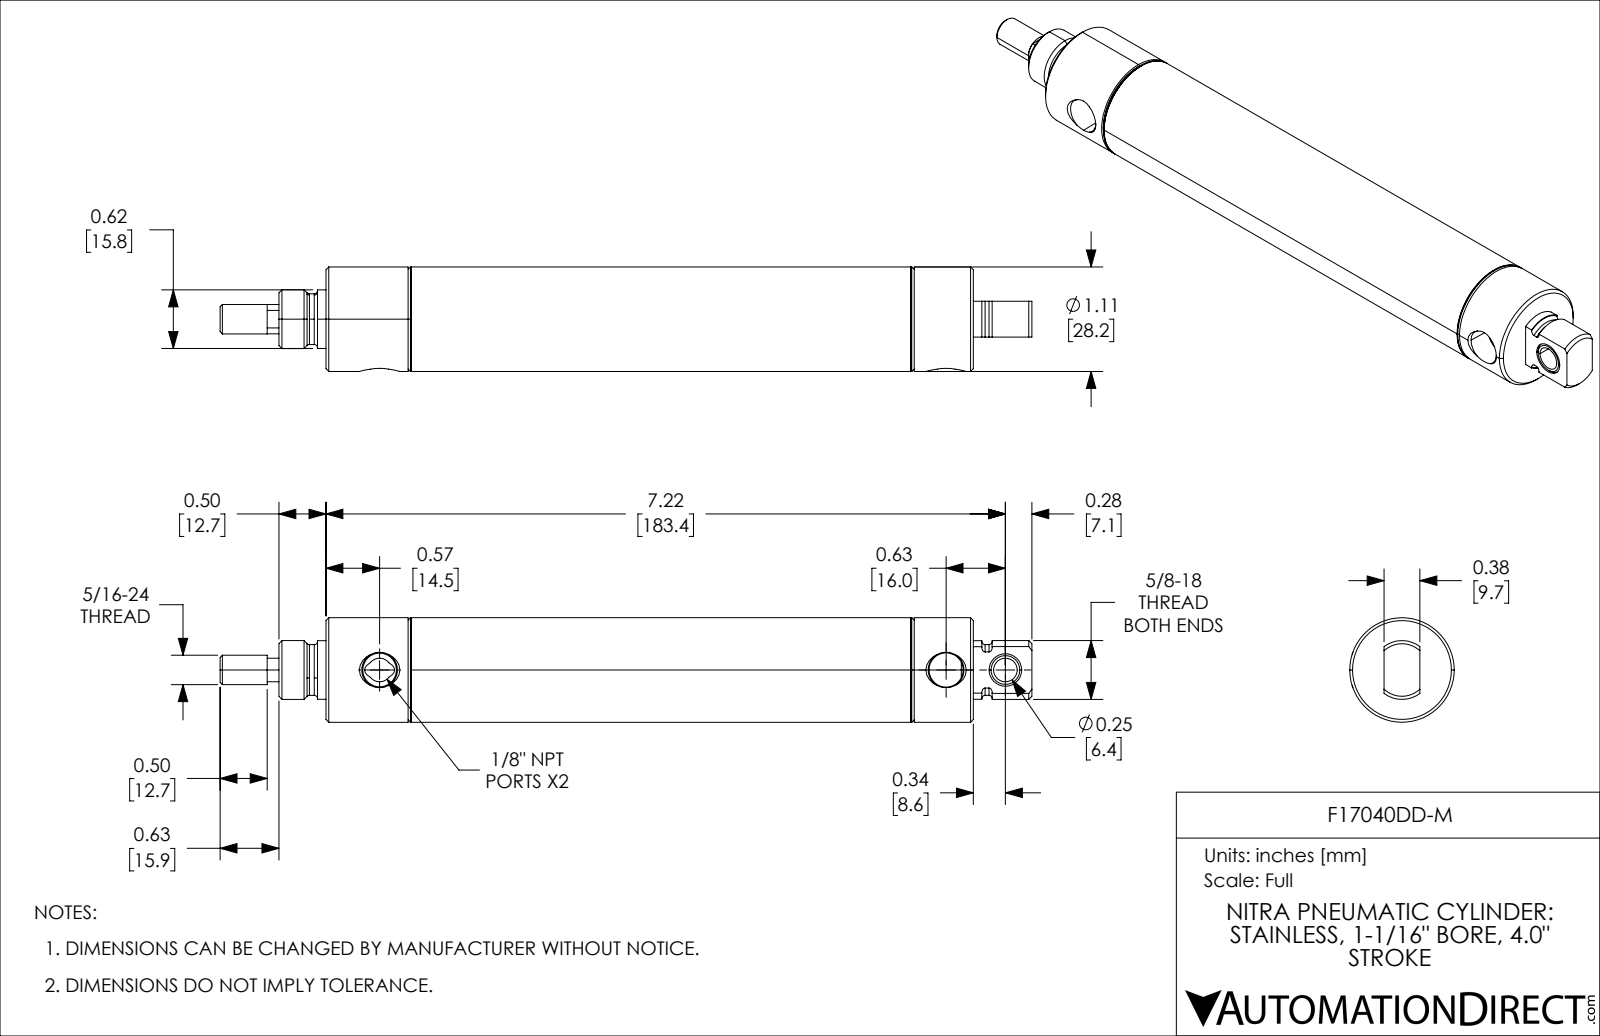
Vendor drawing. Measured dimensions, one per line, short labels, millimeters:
name: F17040DD-M_5; F17040DD-M_11; F17040DD-M_9; F17040DD-M_3 (+2 more)
written by: SolidWorks 2021 (CONFIG_CONTROL_DESIGN)
unit: mm
bodies: 5 solids, 156 faces (30 planar, 58 cylindrical, 68 other)
size: 219.07 × 28.19 × 28.19
volume: 55 133 mm³; area: 42 360 mm²
holes: 1× ⌀6.38, 1× ⌀8.53, 1× ⌀8.78, 1× ⌀9.25, 1× ⌀9.53, 1× ⌀19.05, 1× ⌀25.7
bosses: 1× ⌀28.19, 1× ⌀27.23, 1× ⌀15.88, 1× ⌀15.81, 1× ⌀13.68, 1× ⌀7.94, 1× ⌀7.92
rounds: 1× R3.17, 1× R6.84
face distances: 22.22, 101.6, 123.82, 146.15, 44.55, 22.33, 28.58, 130.18, 152.4, 174.73
hole spacings: 16.01
